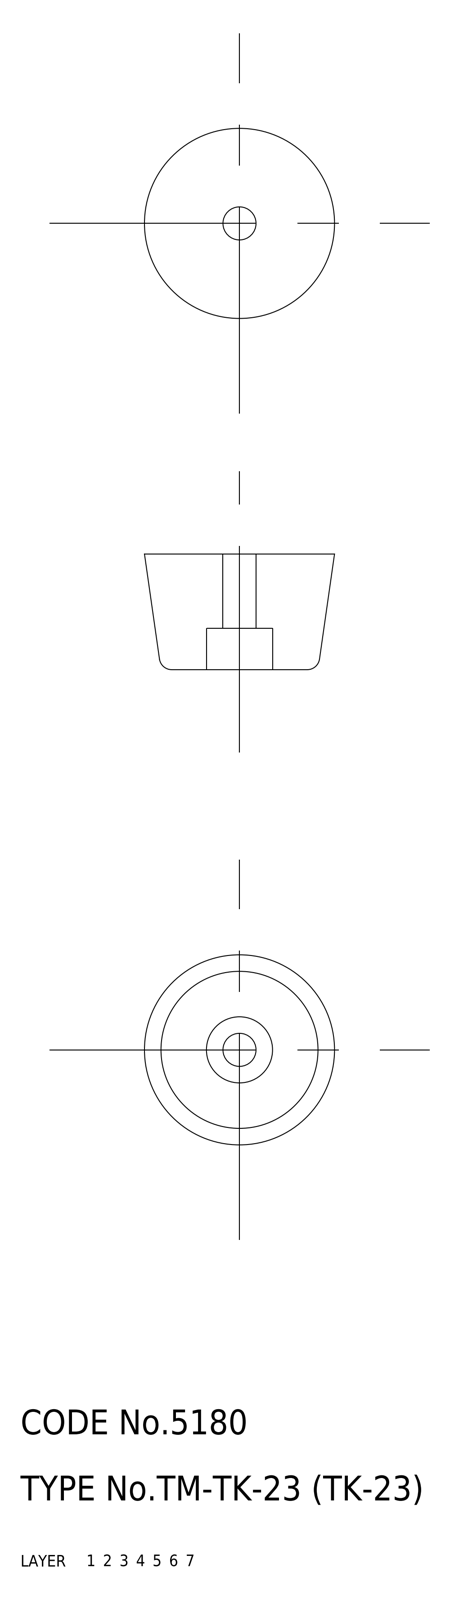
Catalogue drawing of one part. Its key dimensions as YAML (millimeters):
part_name: "washer; rubber foot; TK_23_9408_36"
step_written_by: "CADfix (AUTOMOTIVE_DESIGN)"
units: millimeters
bodies: {solids: 2, faces: 20, planar: 0, cylindrical: 0, other: 20}
overall_size: [23, 23, 14]
volume: 4490
surface_area: 2057
